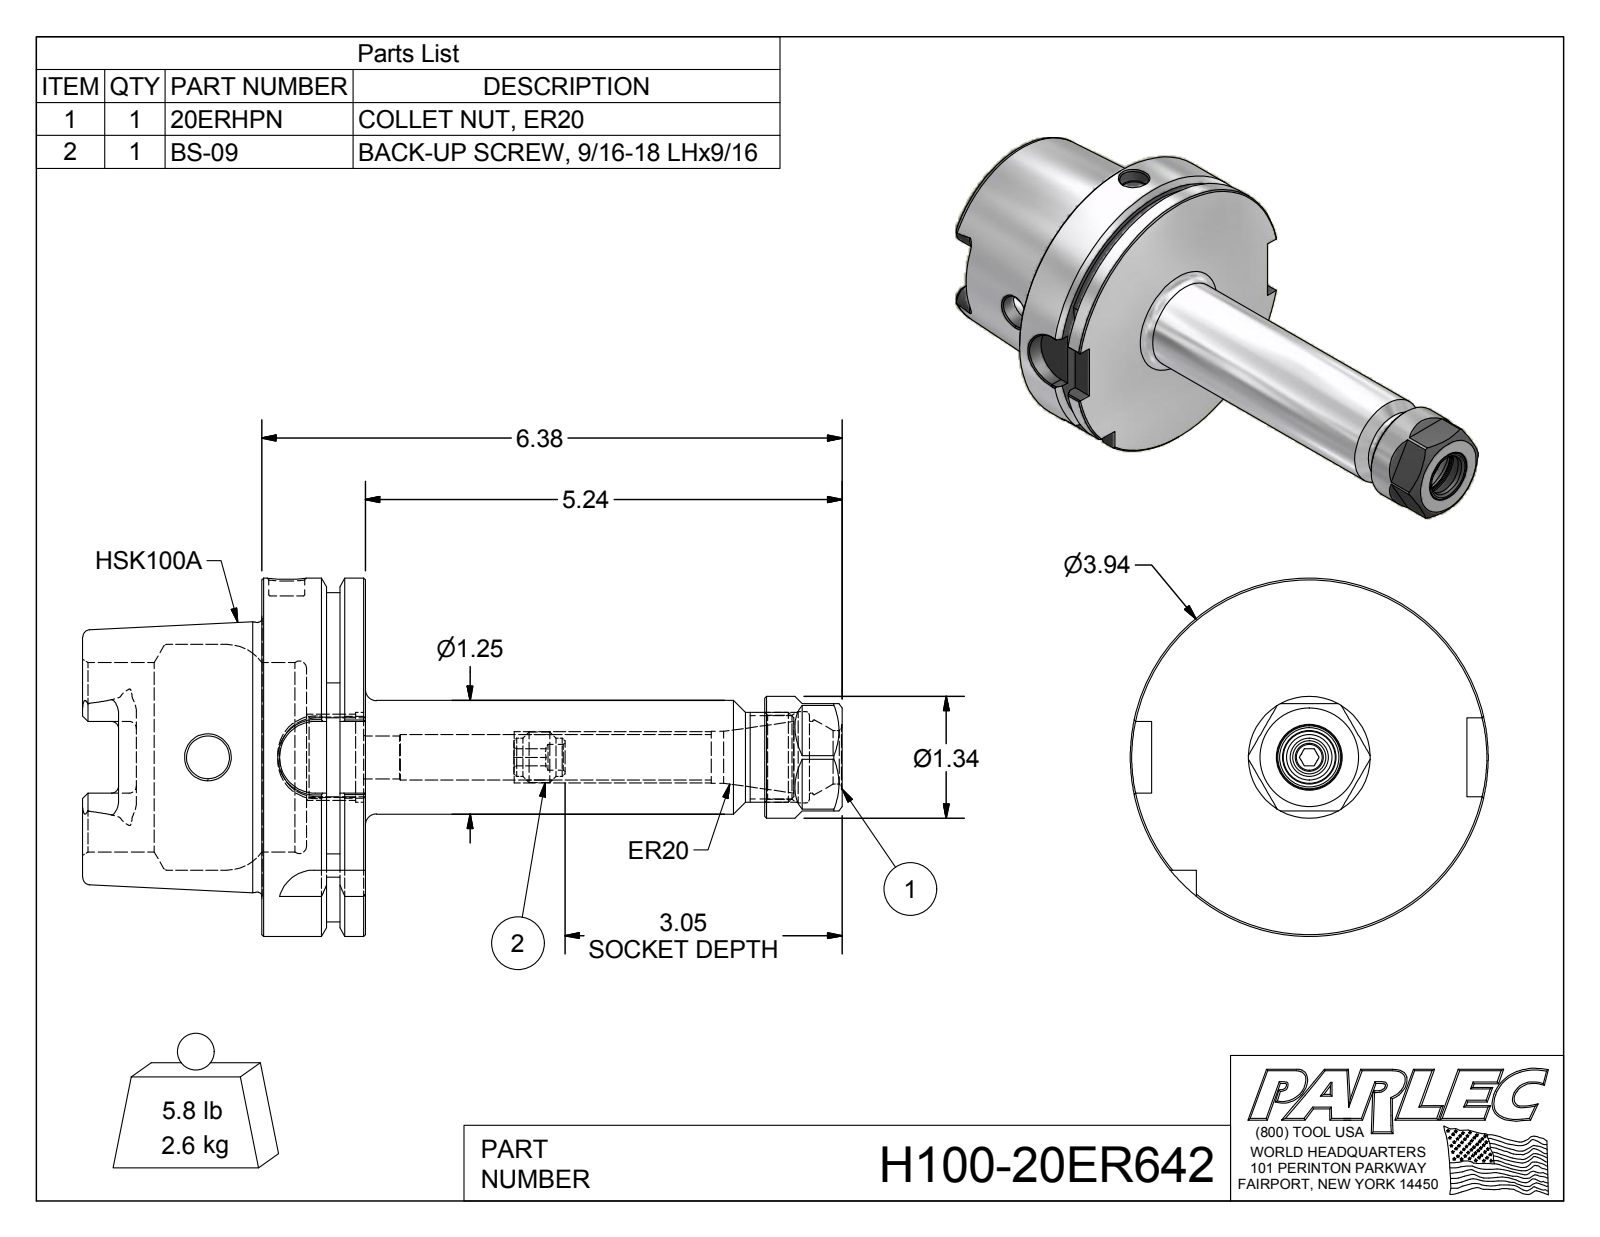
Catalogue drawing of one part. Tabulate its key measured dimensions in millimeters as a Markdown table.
| quantity | value |
| --- | --- |
| part name | H100-20ER642; H100-20ER6-1; BS-09; 20ERHPN |
| STEP written by | Autodesk Inventor 2012 (AUTOMOTIVE_DESIGN) |
| units | millimeters |
| bodies | 3 solids, 187 faces (74 planar, 45 cylindrical, 68 other) |
| overall size | 212.2 × 100 × 100 |
| volume | 337 900 mm³ |
| surface area | 71 870 mm² |
| round holes (diameter × count) | 12 × 2, 7.1 × 1, 10 × 1, 12 × 1, 12.8 × 1, 14.5 × 1, 14.9 × 1, 20.1 × 1, 22.4 × 1, 23.5 × 1, 25 × 1, 25.5 × 1 |
| round bosses / shafts (diameter × count) | 100 × 1, 75.4 × 1, 34 × 1, 31.8 × 1, 25 × 1, 14.1 × 1, 10.7 × 1 |
| partial cylindrical surfaces (radius × count) | 2 × 6, 4.9 × 4, 10 × 4, 46 × 1 |
| main face-to-face distances | 29, 12.5, 16.5, 50, 62.5, 79, 71.9, 21.9, 9.4, 7.1 |
